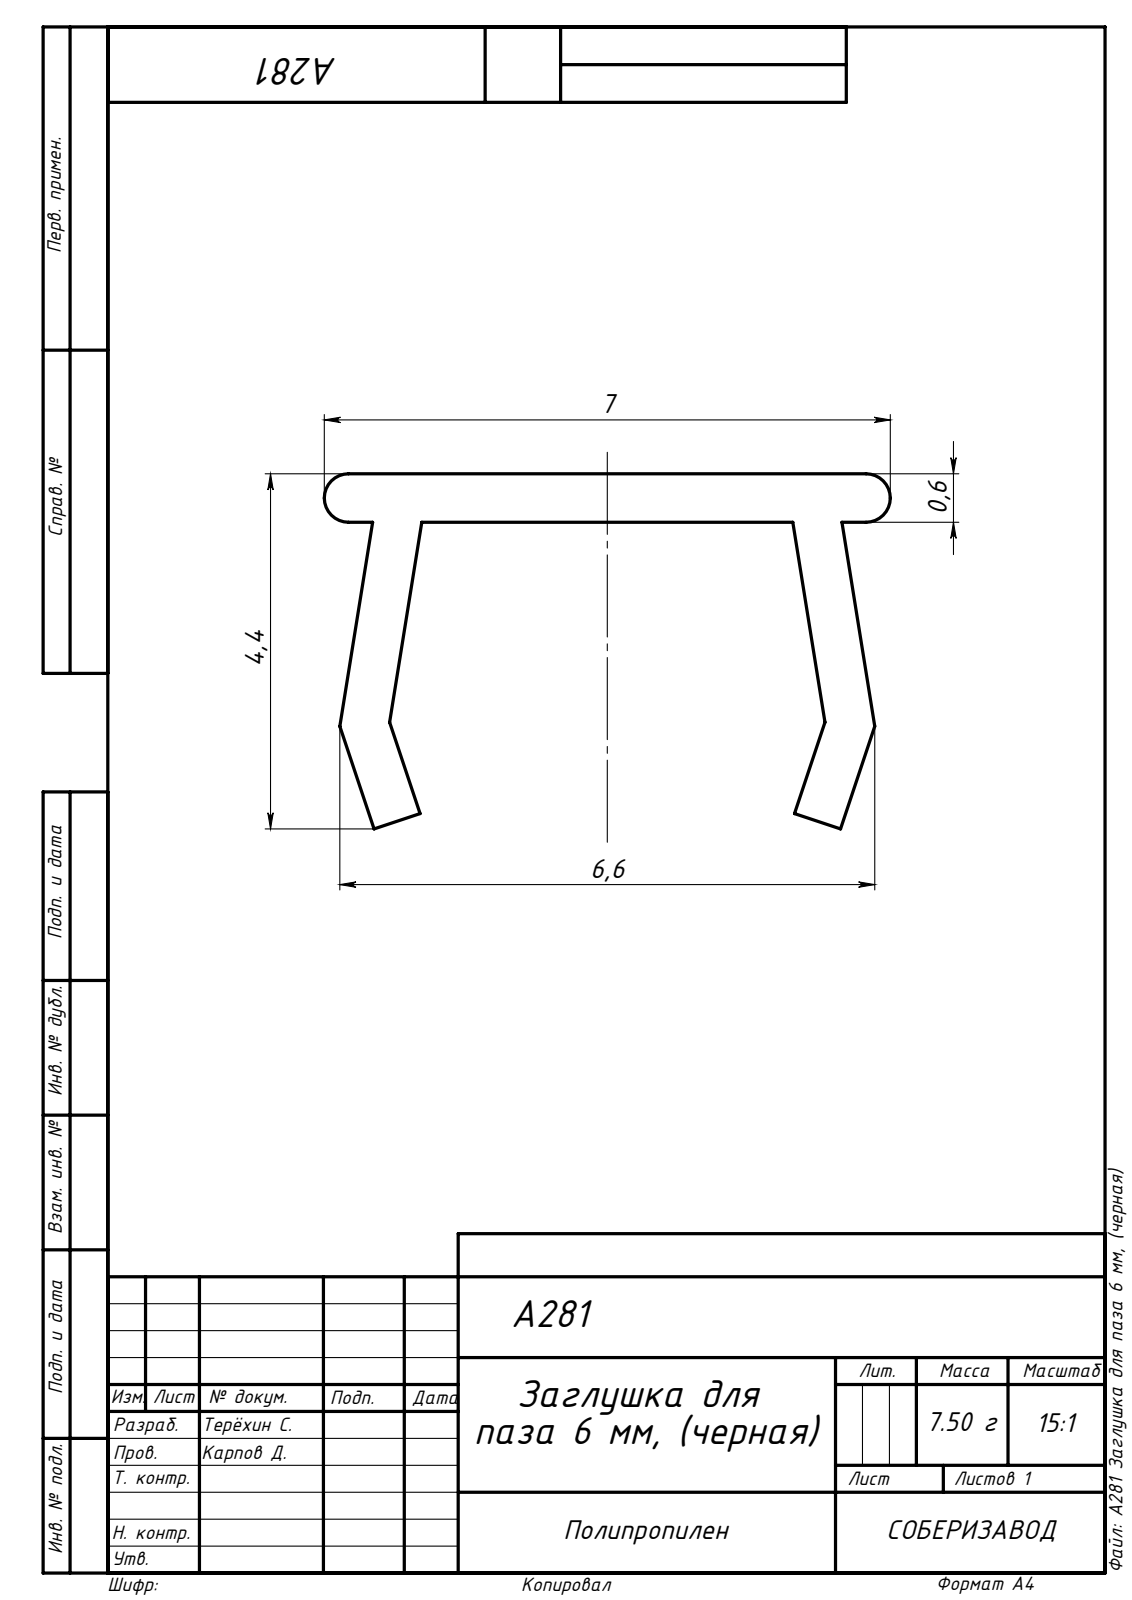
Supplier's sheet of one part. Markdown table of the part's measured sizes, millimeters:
| quantity | value |
| --- | --- |
| part name | A281 Заглушка для паза 6 мм, (черная) |
| STEP written by | SolidWorks 2019 (AUTOMOTIVE_DESIGN) |
| units | millimeters |
| bodies | 1 solid, 20 faces (16 planar, 4 cylindrical, 0 other) |
| overall size | 1000 × 7 × 4 |
| volume | 8 205 mm³ |
| surface area | 28 286 mm² |
| partial cylindrical surfaces (radius × count) | 0.3 × 2 |
| main face-to-face distances | 0.6, 0.61, 1000 |
